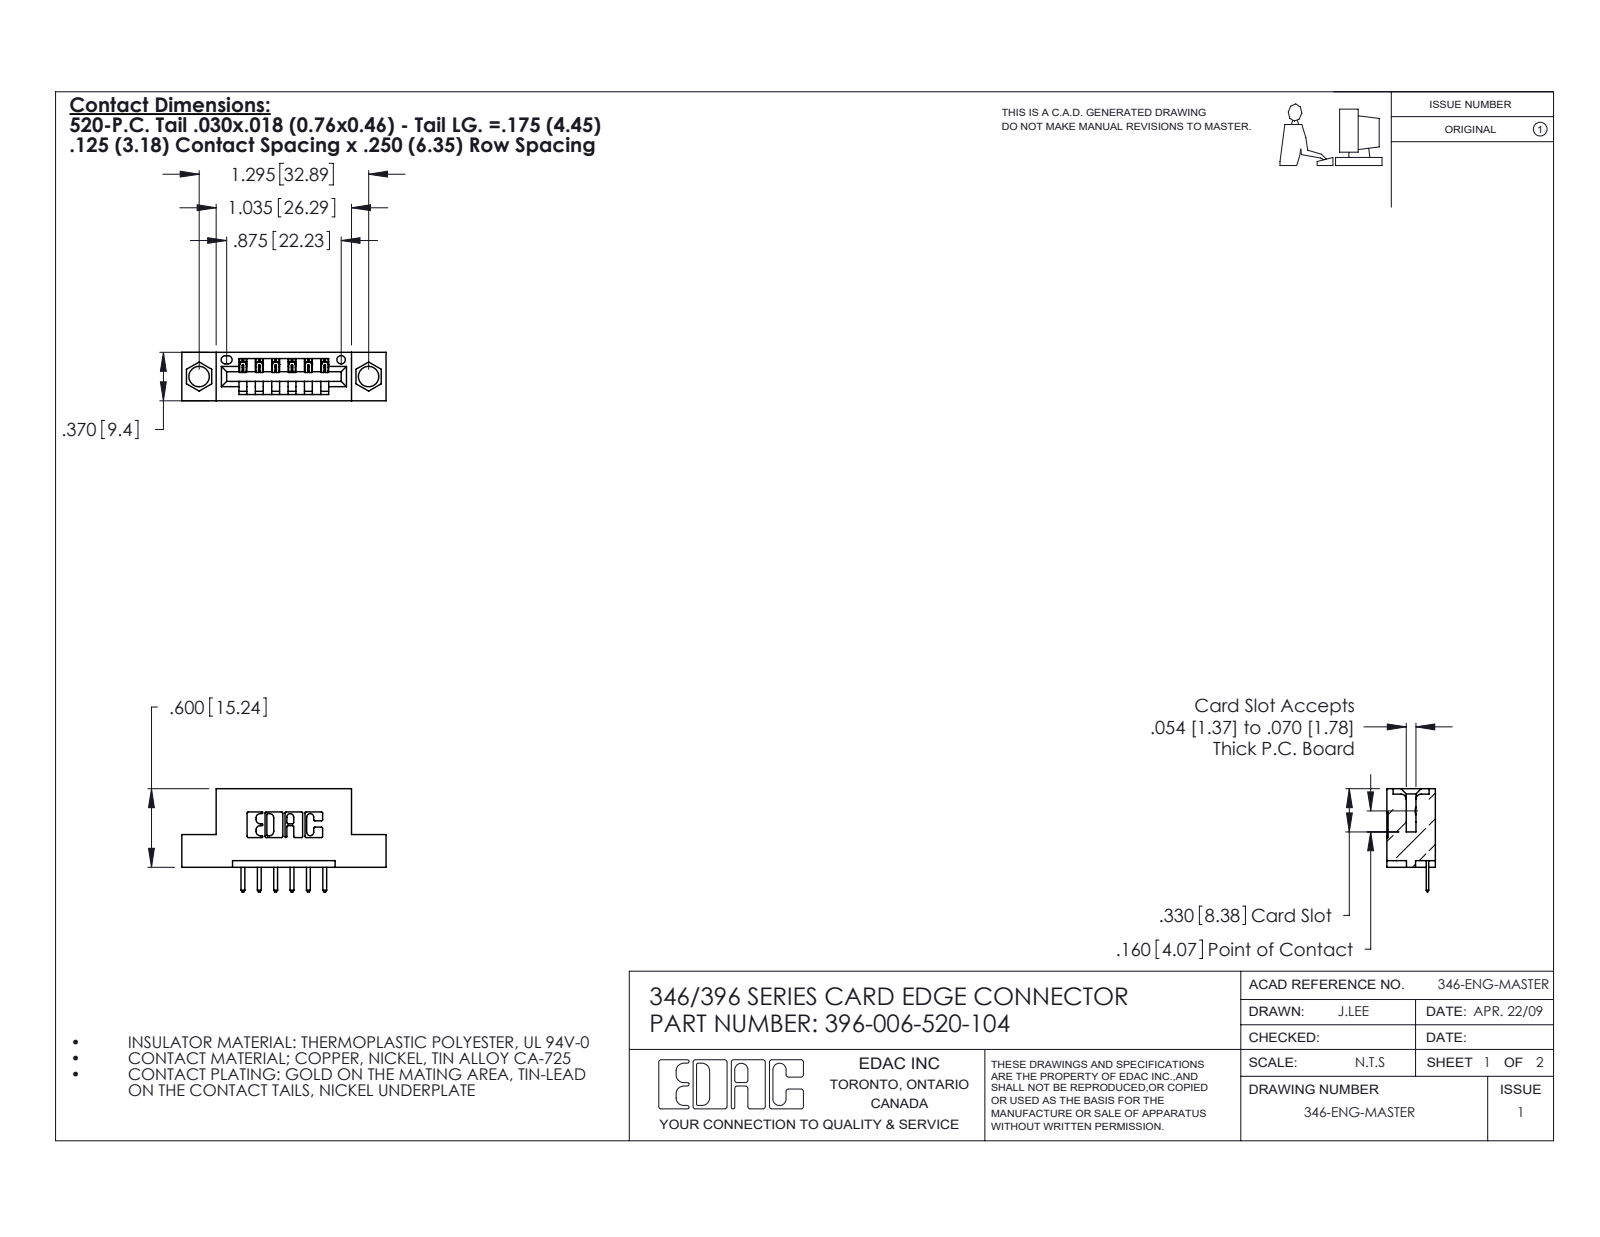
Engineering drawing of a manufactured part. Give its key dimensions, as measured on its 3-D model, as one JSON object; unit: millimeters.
{"part_name": "345-292-001_345-293-120; 346 Part_Flush Mounting Lugs - 0.156 Dia-TH; 396-006-520-104", "step_written_by": "SolidWorks 2020 (CONFIG_CONTROL_DESIGN)", "units": "millimeters", "bodies": {"solids": 7, "faces": 508, "planar": 342, "cylindrical": 166, "other": 0}, "overall_size": [39.6, 20, 9.4], "volume_mm3": 3420, "surface_area_mm2": 3668, "round_holes": [[4, 2], [1.6, 1]], "partial_cylinders_radius": [[0.3, 22], [0.3, 14], [0.2, 12], [0.2, 6], [0.8, 6], [0.7, 3], [0.8, 2], [1, 2]], "face_to_face_distances": [6.4, 9.4, 1.2, 8.2, 3.8, 5.6, 2.5, 4.4, 3.2, 3.2], "hole_center_spacings": [6.2, 27.7, 32.9]}
